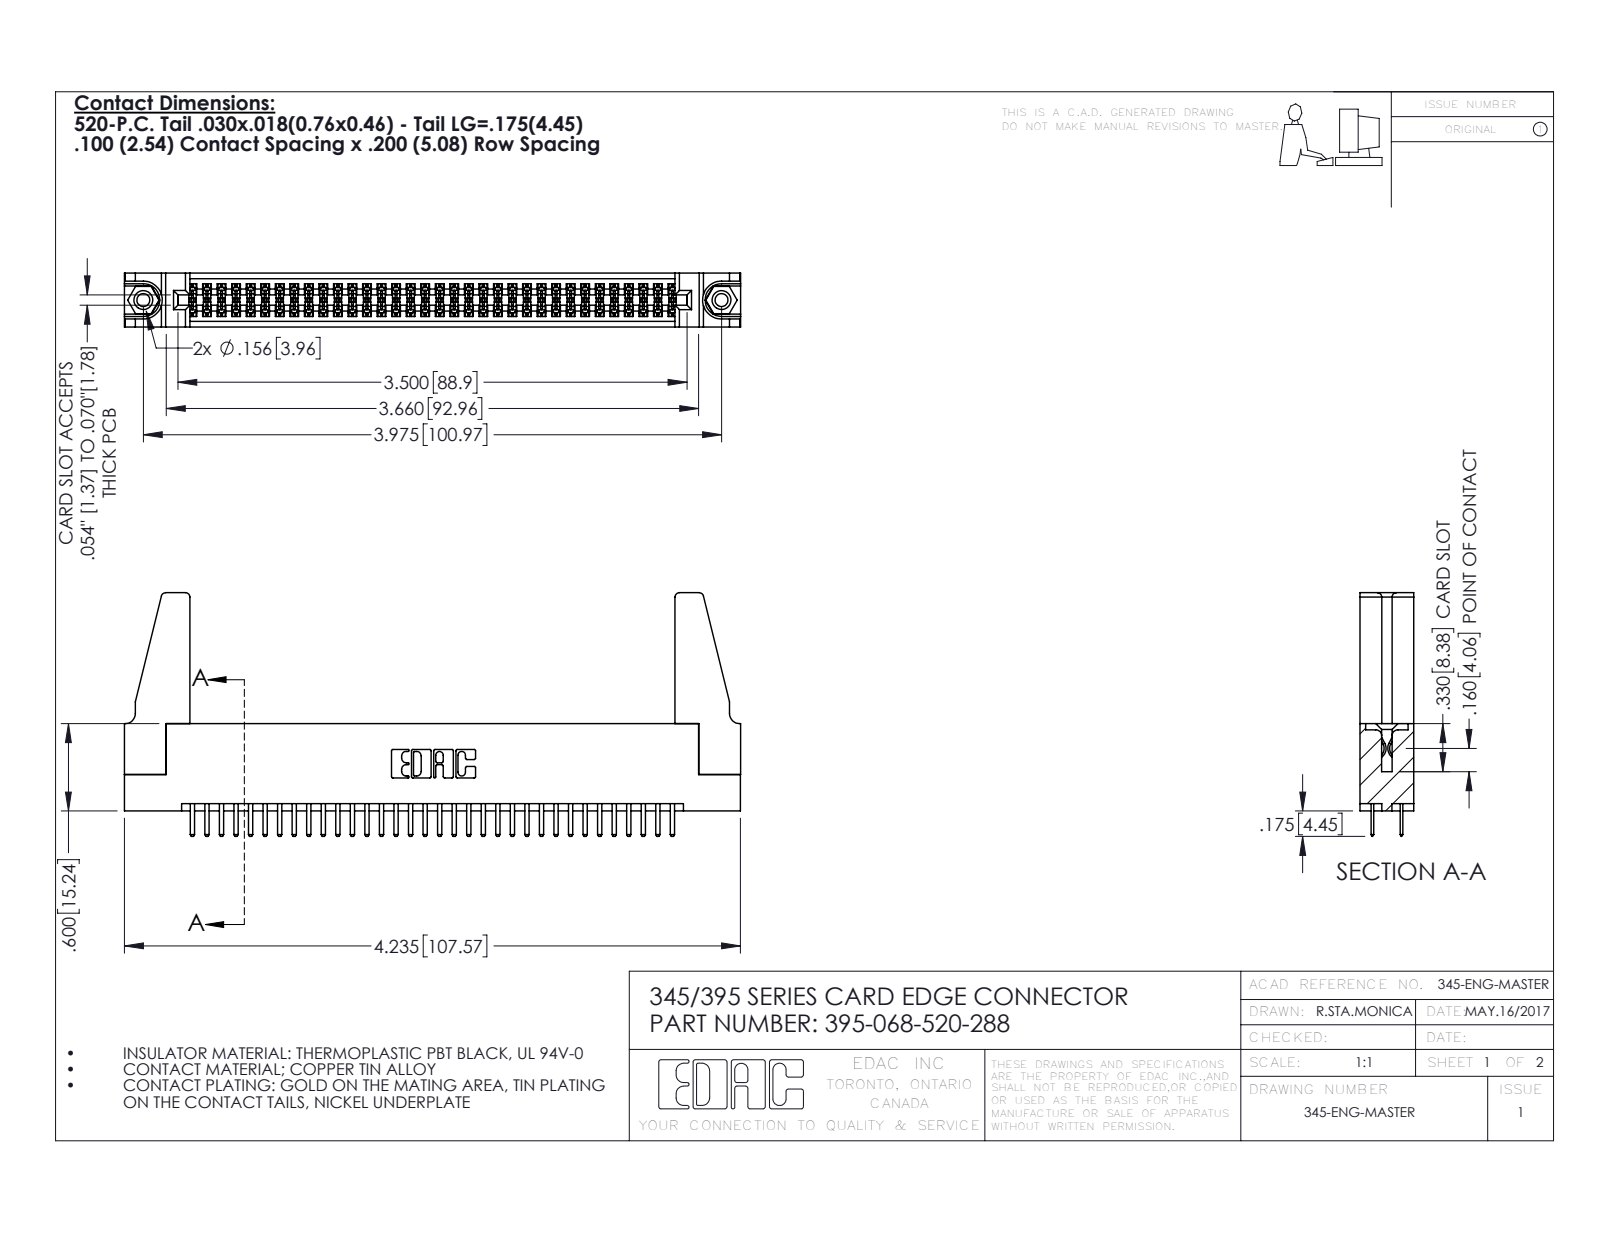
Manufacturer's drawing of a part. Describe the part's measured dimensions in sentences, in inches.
The part is named "345-250-001_345-250-001-102; 395-068-520-288; 345-220-078_345-220-088; 345 Part_Flush Mounting Lugs - 0.156 Dia-TH (+1 more)". Its 3-D file was written by "SolidWorks 2016 (CONFIG_CONTROL_DESIGN)". It is 73 solids with 3922 faces: 2532 planar, 1374 cylindrical and 16 other. Overall it measures 4.236 by 1.675 by 0.37 inches. Its volume is 0.83 cubic inches and its surface area 28.21 square inches. Round holes: 2 of diameter 0.089, 2 of diameter 0.125, 2 of diameter 0.156, 1 of diameter 0.064. Round bosses or shafts: 2 of diameter 0.155. Partial cylindrical surfaces (rounded edges, fillets, slot ends): 102 of radius 0.006, 72 of radius 0.01, 22 of radius 0.01, 8 of radius 0.03, 6 of radius 0.007, 6 of radius 0.031, 3 of radius 0.026, 2 of radius 0.014. The main face-to-face distances are 0.072, 0.298, 0.37, 0.2, 0.098, 0.272, 0.025, 0.225, 0.022, 0.072. The hole center spacings are 0.27, 3.74, 3.975.
